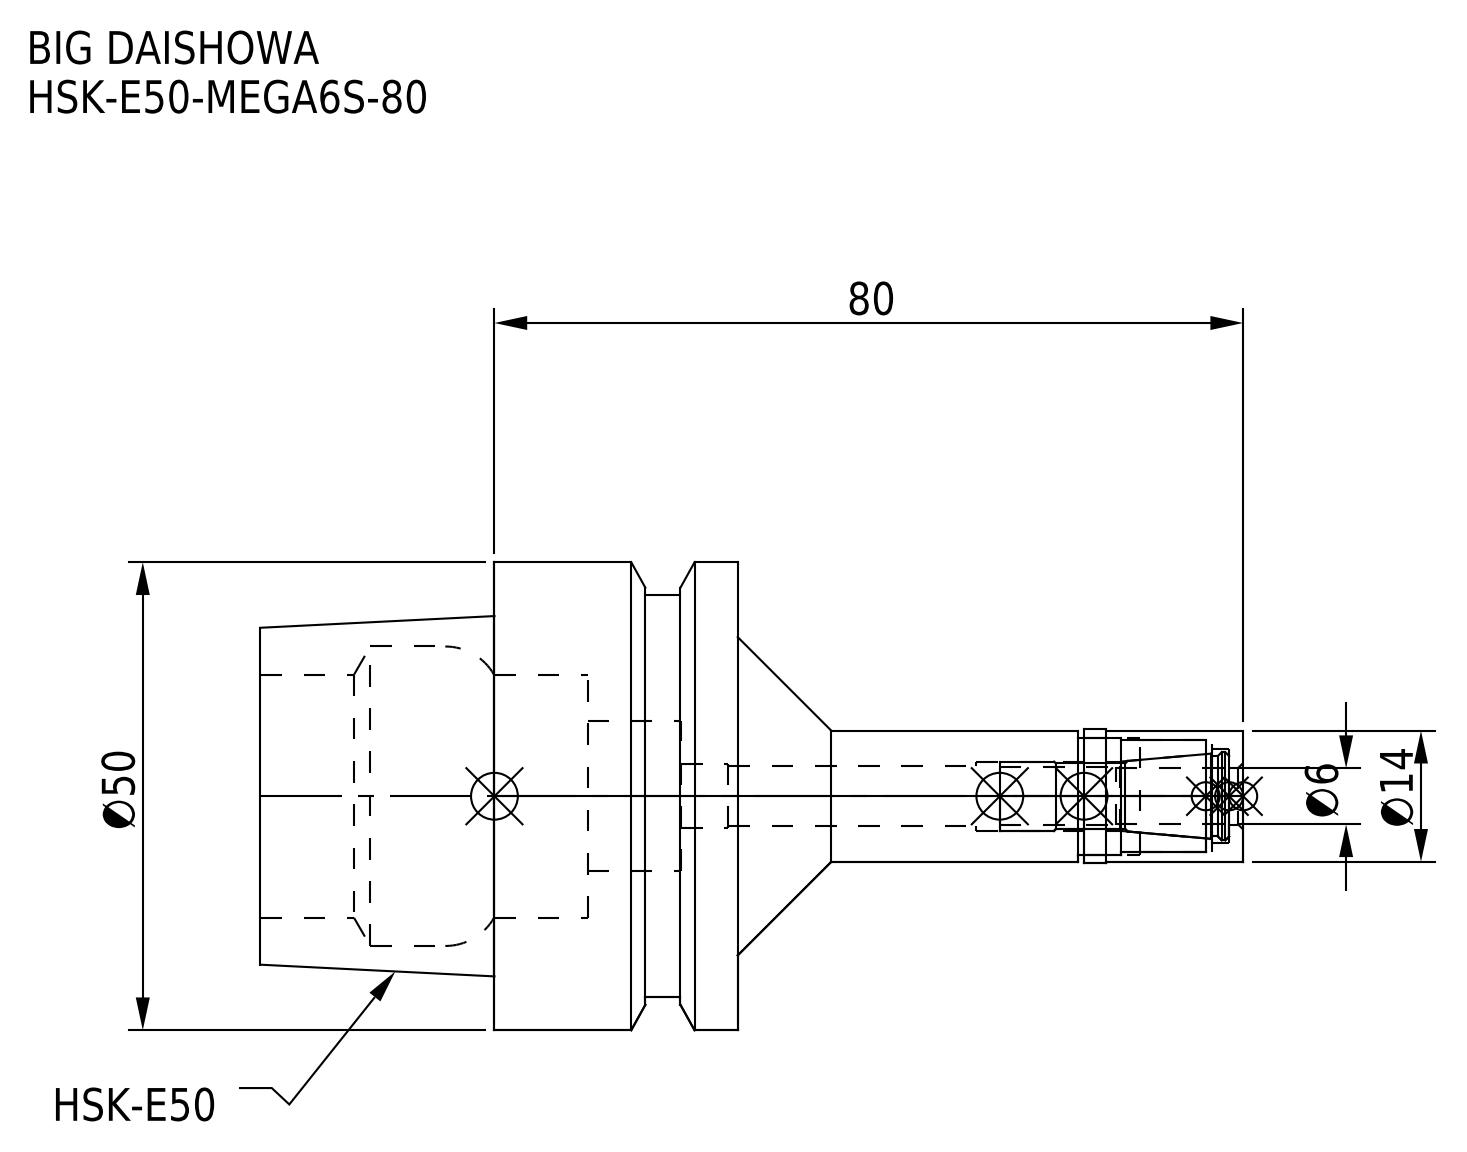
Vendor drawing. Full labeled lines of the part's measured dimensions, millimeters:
Part name (STEP PRODUCT): HSK-E50-MEGA6S-80-060-FreeParts; MGN6S_1.stp; HSK-E50-MEGA6S-80_1.stp; DXF_TEMP_ASSY_ASM_4_ASM.stp (+3 more)
STEP written by: SolidWorks 2019 (CONFIG_CONTROL_DESIGN)
Units: millimetres
Bodies: 2 solids, 74 faces (18 planar, 40 cylindrical, 16 other)
Overall size (bounding box): 105 × 50 × 50
Volume: 60 880 mm³ · Surface area: 19 986 mm²
Round holes (diameter × count): ⌀6.1 ×1, ⌀6.4 ×1, ⌀6.8 ×1, ⌀7.4 ×1, ⌀10 ×1, ⌀12 ×1, ⌀12.5 ×1, ⌀16 ×1, ⌀26 ×1, ⌀32 ×1
Round bosses / shafts (diameter × count): ⌀50 ×1, ⌀43 ×1, ⌀14.3 ×1, ⌀14 ×1
Main face-to-face distances: 26, 51, 25, 16.05, 9.95, 34.95, 6.05, 10, 19.95, 44.95
